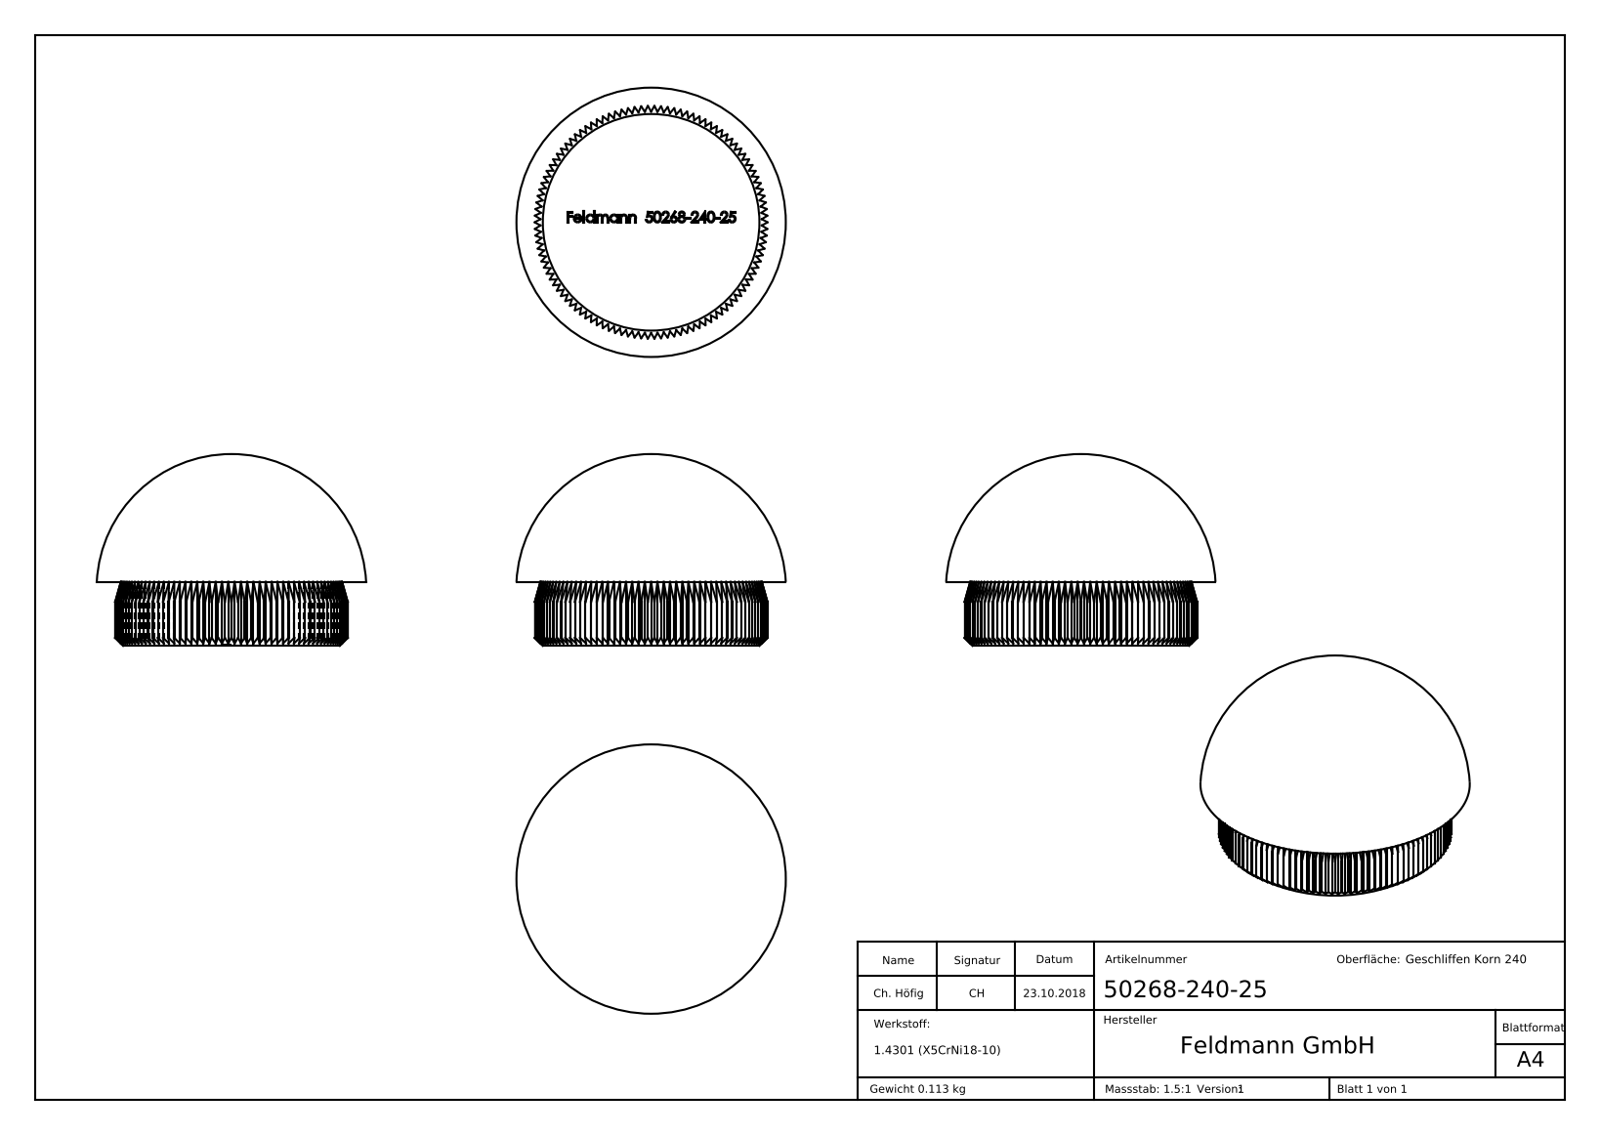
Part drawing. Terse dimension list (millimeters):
name: 50268-240-25
written by: SolidWorks 2015 (CONFIG_CONTROL_DESIGN)
unit: mm
bodies: 1 solid, 584 faces (306 planar, 90 cylindrical, 188 other)
size: 33.7 × 33.7 × 24
volume: 14 333 mm³; area: 3 766 mm²
rounds: 1× R14.55
face distances: 13.85, 8, 13.84, 13.86, 7.9, 6.93, 6.92, 1.32, 5.73, 5.61
